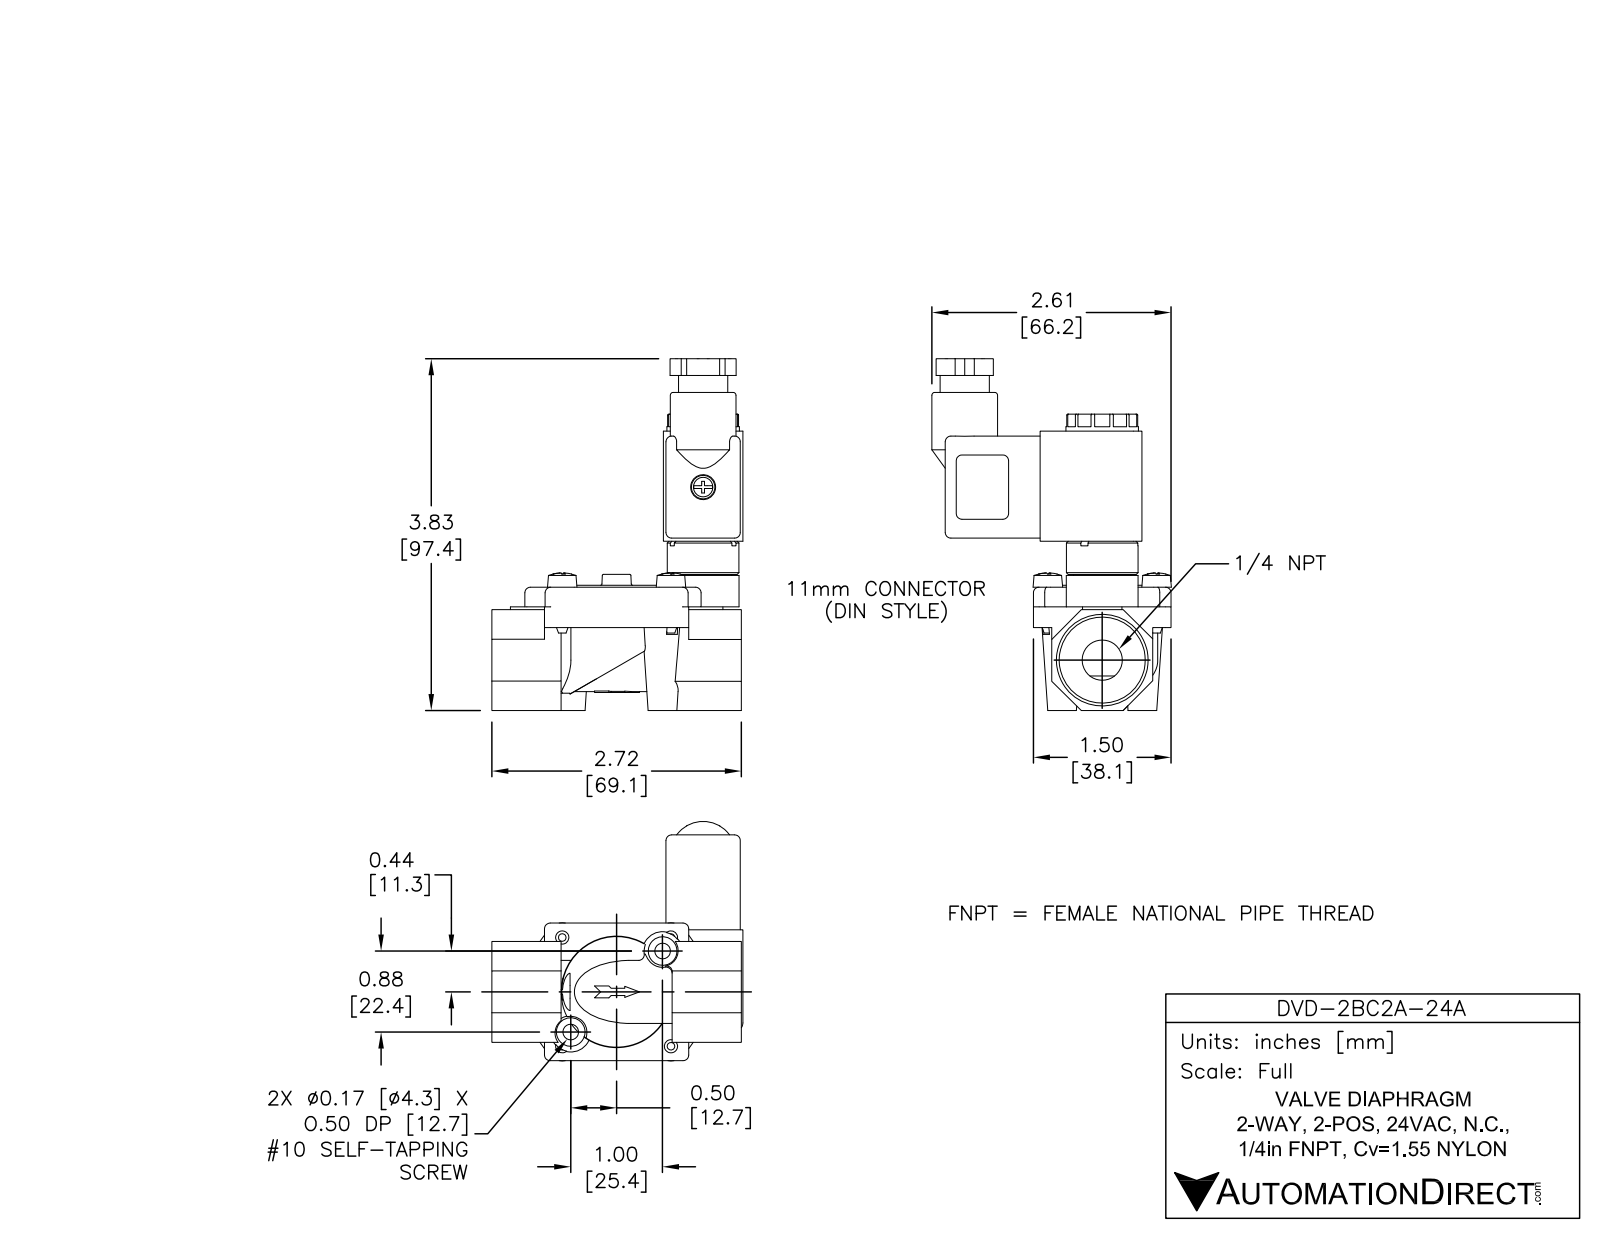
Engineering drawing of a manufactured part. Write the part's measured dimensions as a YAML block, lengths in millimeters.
part_name: "DVD-2BC2A-24A"
step_written_by: "SolidWorks 2015 (AUTOMOTIVE_DESIGN)"
units: millimeters
bodies: {solids: 11, faces: 1418, planar: 715, cylindrical: 244, other: 459}
overall_size: [97.4, 69.5, 66.3]
volume: 69600
surface_area: 39250
round_holes:
  - {diameter: 3.7, count: 4}
  - {diameter: 4.2, count: 4}
  - {diameter: 1.5, count: 2}
  - {diameter: 2.4, count: 2}
  - {diameter: 4.3, count: 2}
  - {diameter: 1.6, count: 1}
  - {diameter: 4, count: 1}
  - {diameter: 4.2, count: 1}
  - {diameter: 6.4, count: 1}
  - {diameter: 6.9, count: 1}
  - {diameter: 7.9, count: 1}
  - {diameter: 8, count: 1}
round_bosses_or_shafts:
  - {diameter: 4.7, count: 4}
  - {diameter: 3.2, count: 4}
  - {diameter: 15.9, count: 2}
  - {diameter: 34.9, count: 1}
  - {diameter: 20.1, count: 1}
  - {diameter: 19.9, count: 1}
  - {diameter: 19.8, count: 1}
  - {diameter: 18.2, count: 1}
partial_cylinders:
  - {radius: 0.3, count: 24}
  - {radius: 1.6, count: 24}
  - {radius: 4, count: 12}
  - {radius: 1.1, count: 3}
  - {radius: 2.4, count: 2}
  - {radius: 5.5, count: 2}
  - {radius: 7.7, count: 1}
  - {radius: 8.7, count: 1}
face_to_face_distances: [1.3, 27.9, 22, 19.3, 5.1, 33, 20, 2, 2, 18]
hole_center_spacings: [21.3, 30.1, 4.6, 16.9, 17.5, 26.3, 28, 38.2]
